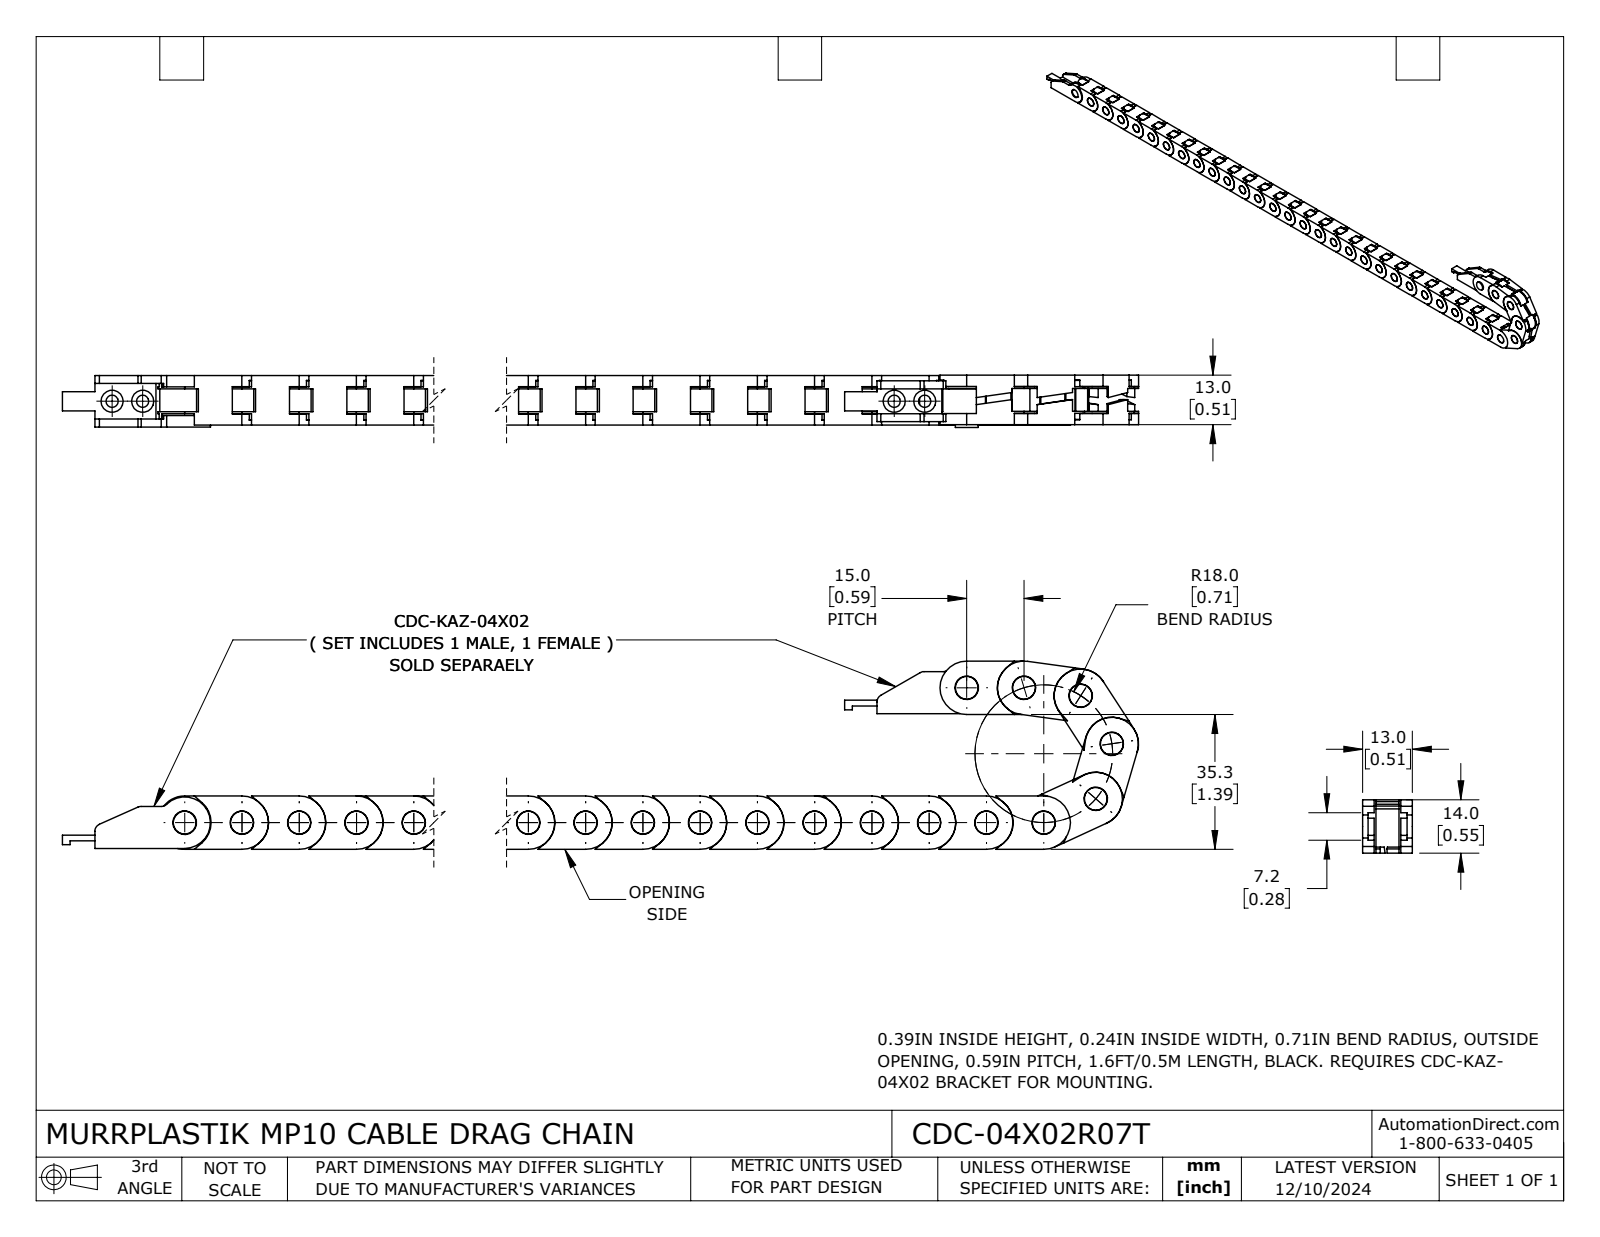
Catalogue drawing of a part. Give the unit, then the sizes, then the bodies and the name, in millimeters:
Units: millimetres
Overall size (bounding box): 476.8 × 49.3 × 13.7
Round holes (diameter × count): ⌀6.1 ×33, ⌀3.2 ×4, ⌀6.2 ×1
Round bosses / shafts (diameter × count): ⌀6 ×34, ⌀14 ×32
Partial cylindrical surfaces — rounded edges, fillets, slot ends (radius × count): R0.5 ×165, R7 ×34, R3.6 ×33, R11.6 ×33, R2 ×6, R1 ×2, R6.8 ×2, R7 ×2
Main face-to-face distances: 3.5, 9.5, 13, 2.2, 11.7, 1.3, 8.2, 6, 3.4, 0.5
Hole centre spacings: 15, 30, 45, 60, 75, 90, 105, 120
Volume: 53 180 mm³ · Surface area: 76 000 mm²
Bodies: 35 solids, 2373 faces (1607 planar, 762 cylindrical, 4 other)
Part name (STEP PRODUCT): CDC-04X02R07T
STEP written by: SolidWorks 2024 (AUTOMOTIVE_DESIGN)
